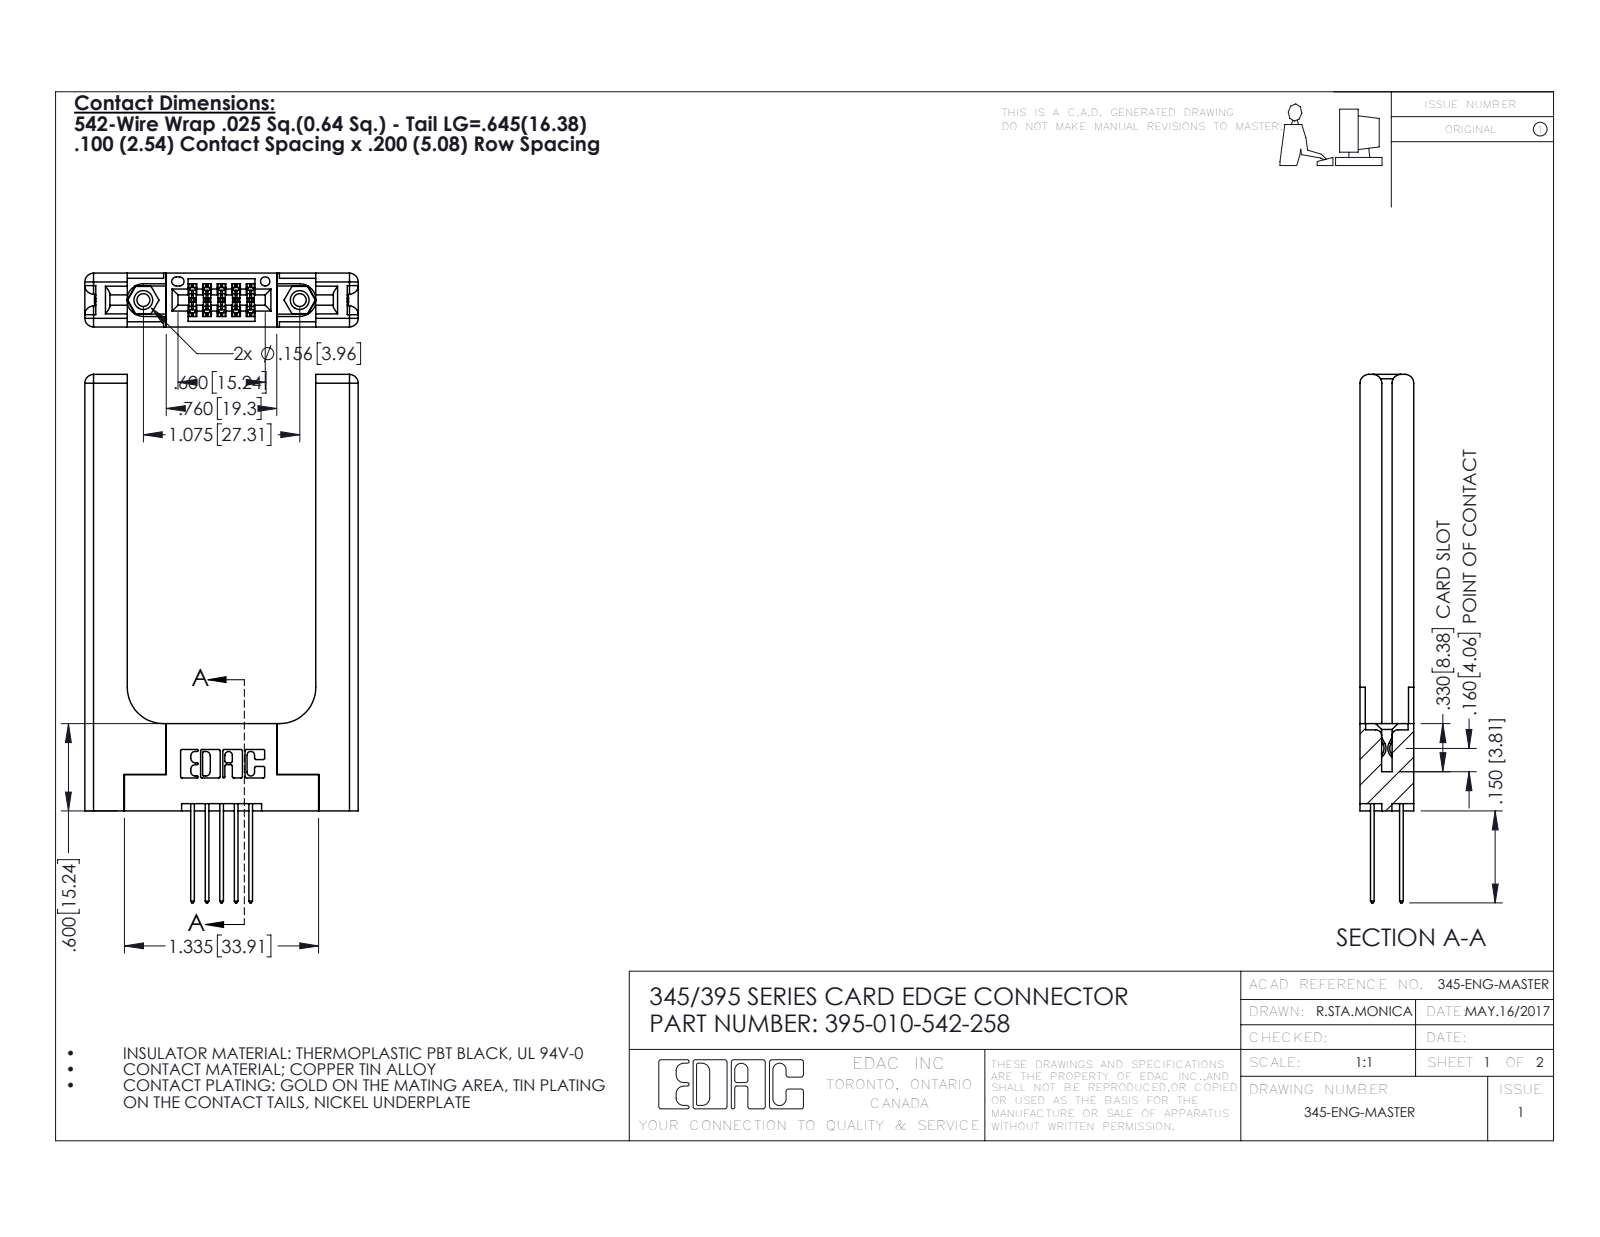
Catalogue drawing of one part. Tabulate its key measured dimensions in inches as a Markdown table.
| quantity | value |
| --- | --- |
| part name | 345-292-001_345-293-142; 345-250-001_345-250-001-102; 395-010-542-258; 345-220-058_345-220-058 (+1 more) |
| STEP written by | SolidWorks 2016 (CONFIG_CONTROL_DESIGN) |
| units | inches |
| bodies | 15 solids, 882 faces (558 planar, 264 cylindrical, 60 other) |
| overall size | 3.632 × 1.879 × 0.37 |
| volume | 0.782 in³ |
| surface area | 17.01 in² |
| round holes (diameter × count) | 0.089 × 2, 0.125 × 2, 0.156 × 2, 0.064 × 1 |
| round bosses / shafts (diameter × count) | 0.155 × 2 |
| partial cylindrical surfaces (radius × count) | 0.01 × 22, 0.06 × 16, 0.006 × 15, 0.01 × 10, 0.007 × 6, 0.031 × 6, 0.026 × 3, 0.014 × 2 |
| main face-to-face distances | 0.37, 0.15, 0.22, 0.072, 0.077, 0.148, 0.298, 1.296, 0.2, 0.071 |
| hole center spacings | 0.27, 0.847, 1.075 |
